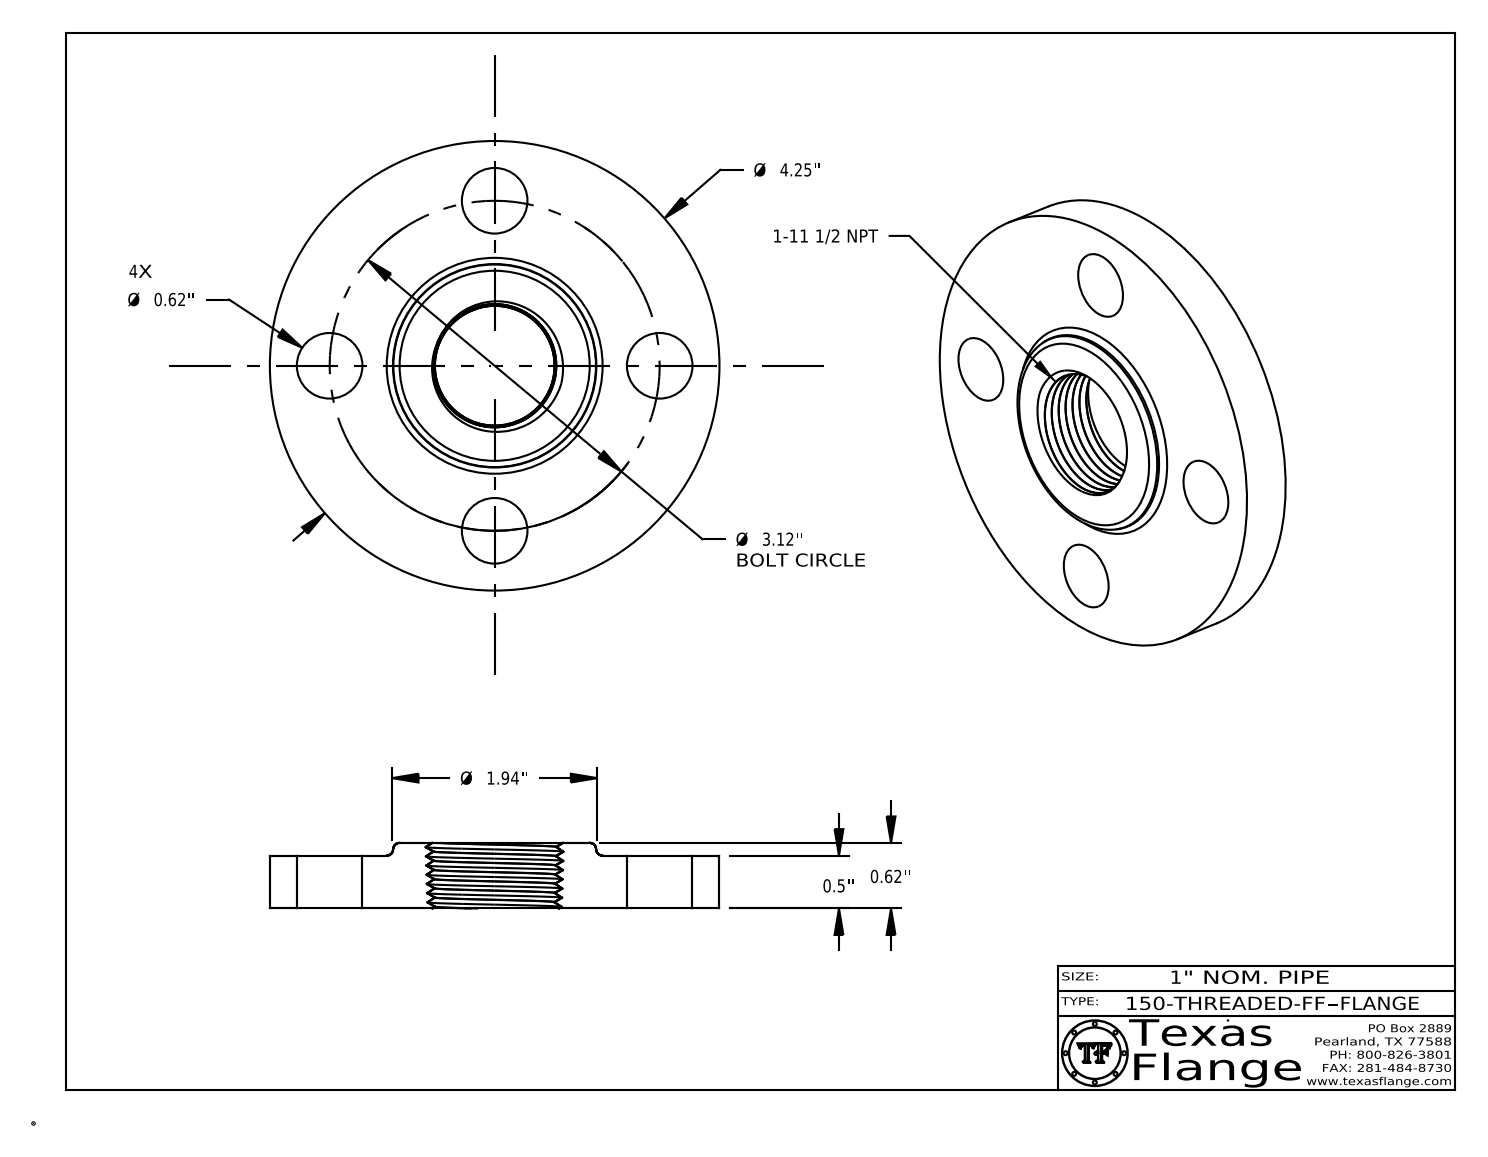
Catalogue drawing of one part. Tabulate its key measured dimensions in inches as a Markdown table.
| quantity | value |
| --- | --- |
| part name | 150-THREADED-FF |
| STEP written by | CATIA V5 STEP AP214 (AUTOMOTIVE_DESIGN) |
| units | inches |
| bodies | 1 solid, 483 faces (368 planar, 30 cylindrical, 85 other) |
| overall size | 4.25 × 4.25 × 0.62 |
| volume | 6.116 in³ |
| surface area | 39.13 in² |
| round holes (diameter × count) | 0.62 × 4, 0.495 × 1 |
| round bosses / shafts (diameter × count) | 0.03 × 8, 4.25 × 1, 0.39 × 1 |
| main face-to-face distances | 0.5, 0.62, 0.12, 0.485, 0.015, 0.135, 0.148, 0.144, 0.027, 0.122 |
| hole center spacings | 2.206, 1.194, 2.882, 3.12 |
